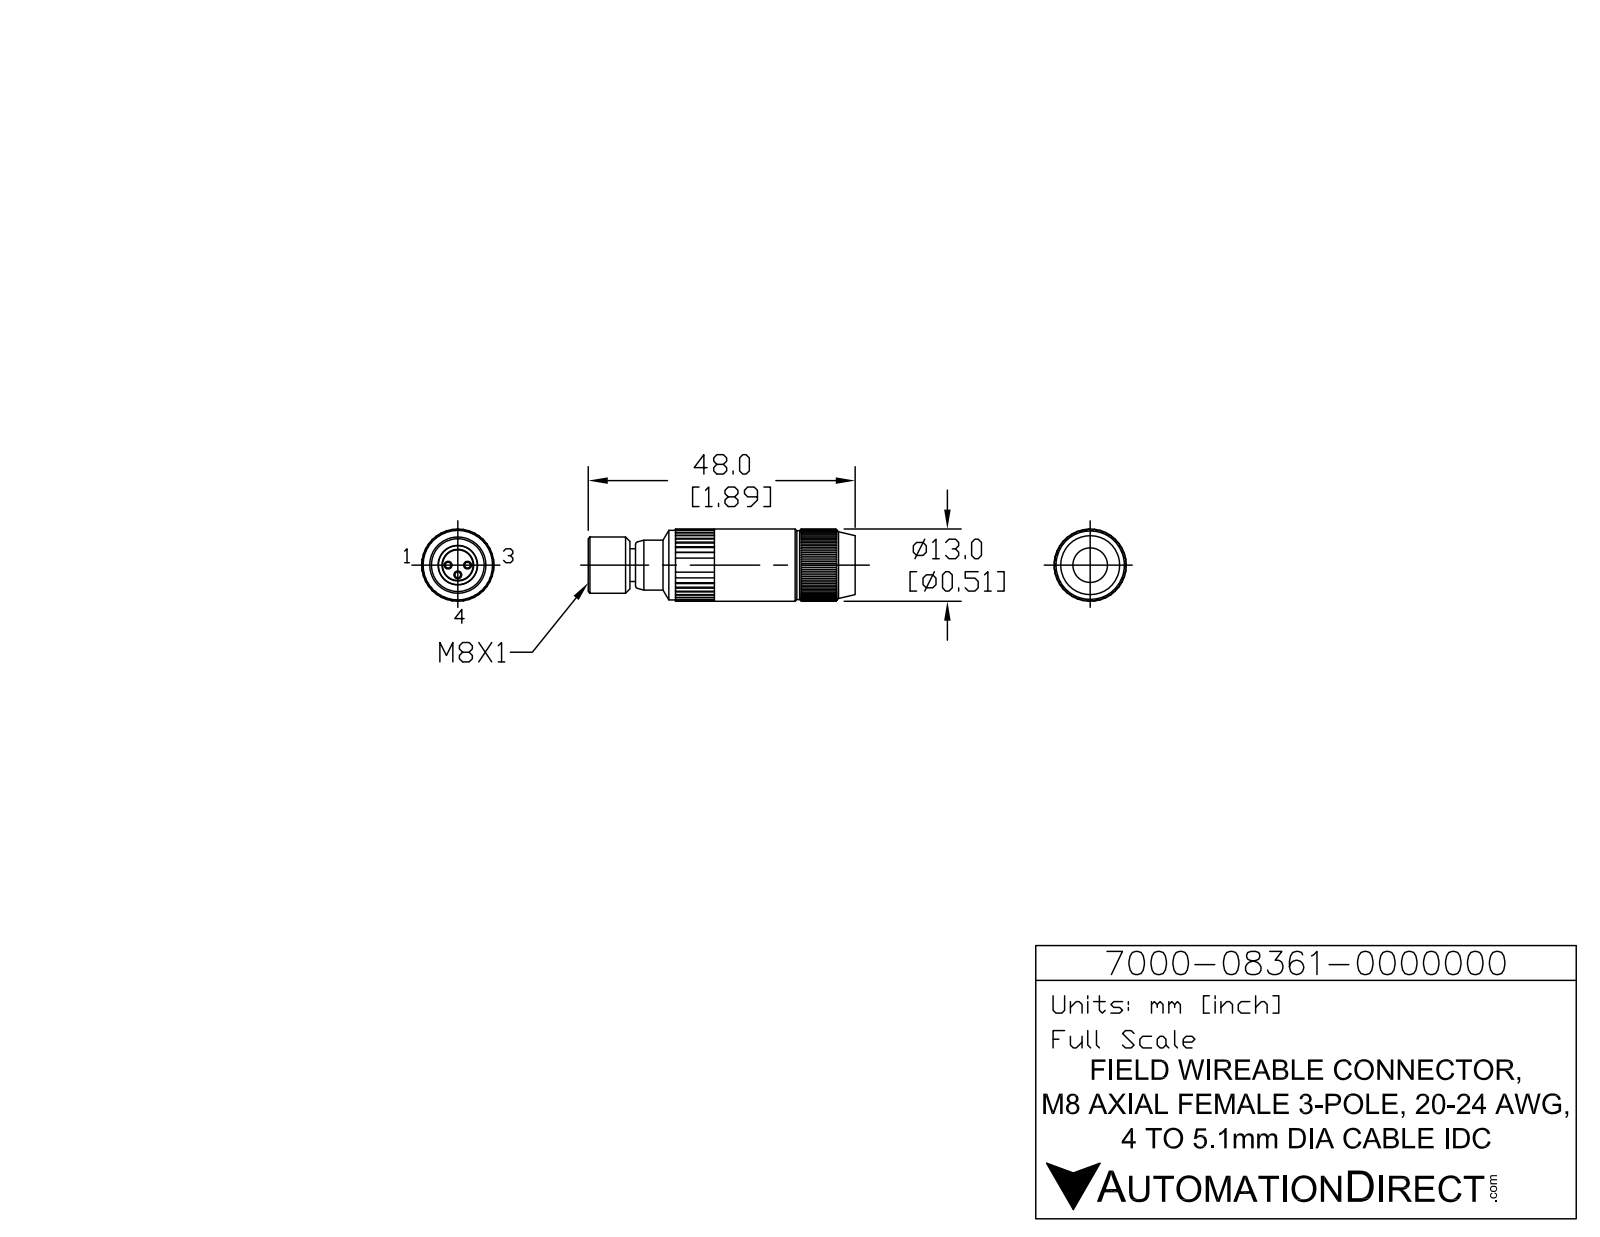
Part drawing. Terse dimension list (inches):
name: 7000-08361-0000000
written by: SolidWorks 2015 (AUTOMOTIVE_DESIGN)
unit: in
bodies: 1 solid, 678 faces (422 planar, 170 cylindrical, 86 other)
size: 1.89 × 0.512 × 0.512
volume: 0.295 in³; area: 4.325 in²
holes: 3× ⌀0.039, 1× ⌀0.23, 1× ⌀0.318
bosses: 1× ⌀0.512, 1× ⌀0.488, 1× ⌀0.478, 1× ⌀0.472, 1× ⌀0.354, 1× ⌀0.268, 1× ⌀0.228
rounds: 1× R0.201
face distances: 0.184, 1.89, 1.594, 0.295, 0.394, 1.496, 1.201, 0.969, 0.575, 0.626
hole spacings: 0.081, 0.098, 0.079, 0.157
